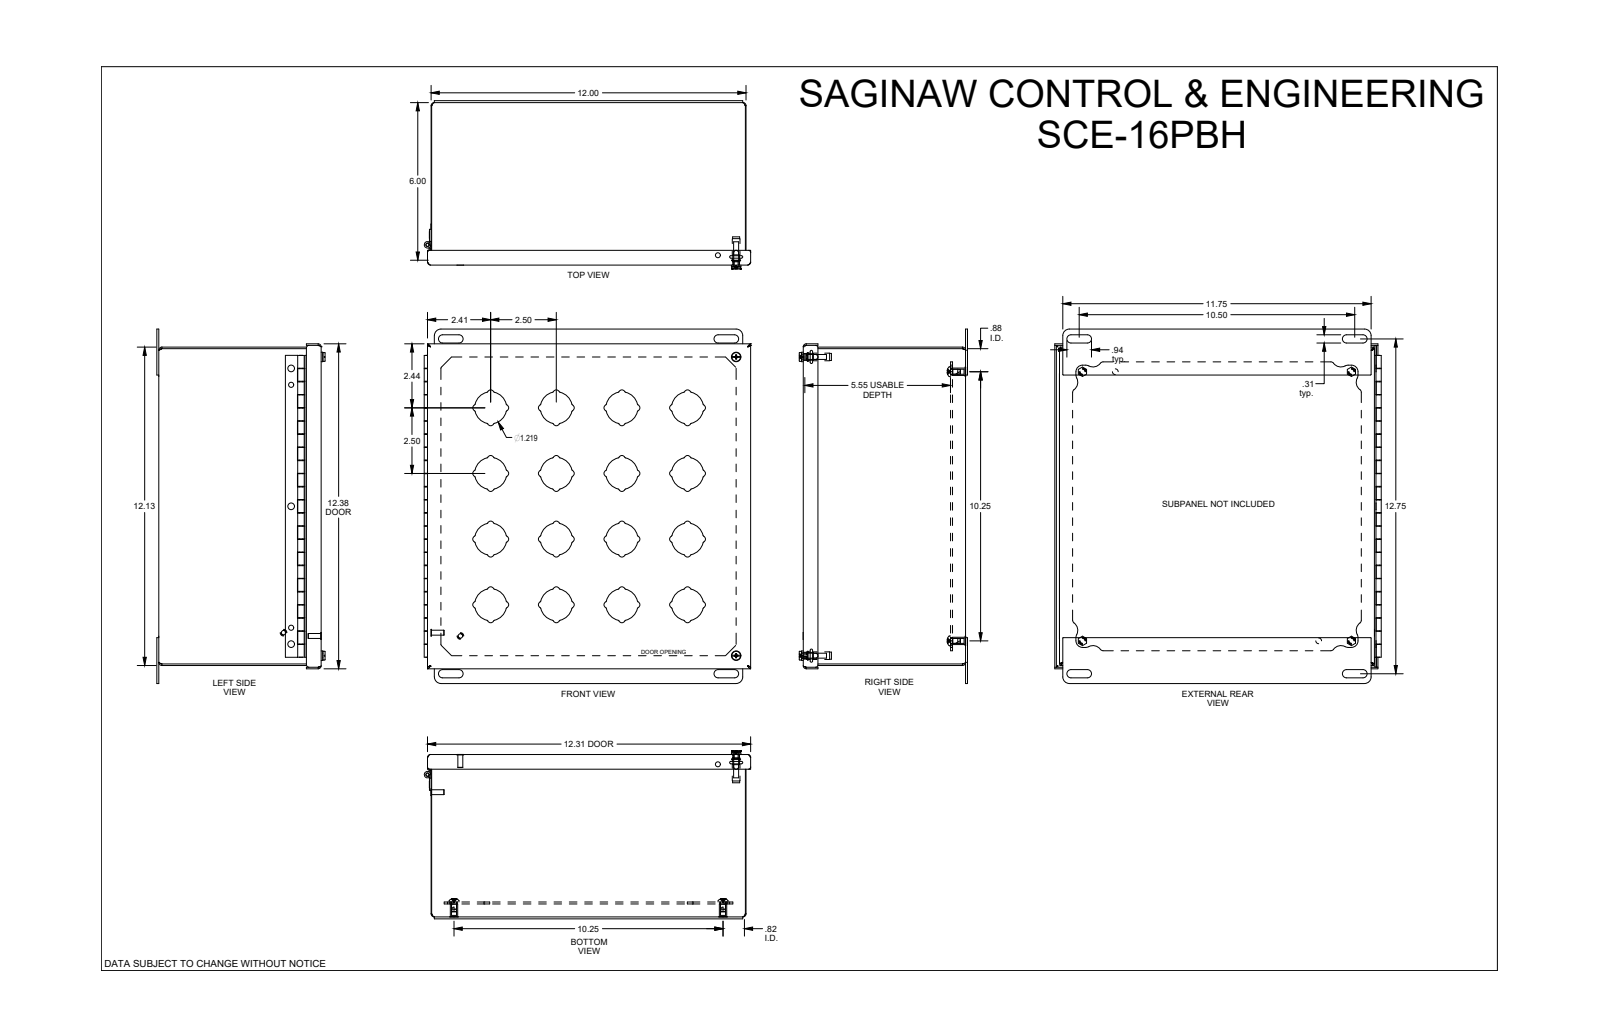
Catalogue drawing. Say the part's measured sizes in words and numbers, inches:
The part is named "SCE-16PBH". Its 3-D file was written by "SolidWorks 2021 (AUTOMOTIVE_DESIGN)". It is 7 solids with 1119 faces: 402 planar, 565 cylindrical and 152 other. Overall it measures 13.5 by 12.438 by 6.322 inches. Its volume is 52.66 cubic inches and its surface area 1 586 square inches. Round holes: 9 of diameter 0.19, 6 of diameter 0.25, 4 of diameter 0.281, 4 of diameter 0.317, 2 of diameter 0.126, 2 of diameter 0.193, 2 of diameter 0.218, 2 of diameter 0.22, 2 of diameter 0.266, 1 of diameter 0.193. Round bosses or shafts: 5 of diameter 0.188, 4 of diameter 0.437, 4 of diameter 0.28, 4 of diameter 0.256, 2 of diameter 0.362, 2 of diameter 0.292, 2 of diameter 0.27, 2 of diameter 0.26. Partial cylindrical surfaces (rounded edges, fillets, slot ends): 128 of radius 0.04, 72 of radius 0.125, 20 of radius 0.06, 18 of radius 0.01, 16 of radius 0.25, 16 of radius 0.609, 8 of radius 0.063, 8 of radius 0.156. The main face-to-face distances are 0.06, 6.125, 12.065, 11.94, 6.065, 6.185, 0.435, 0.075, 0.495, 5.63. The hole center spacings are 10.25, 10.764, 0.752, 9.517, 10.765, 10.824, 11.25, 15.247.
